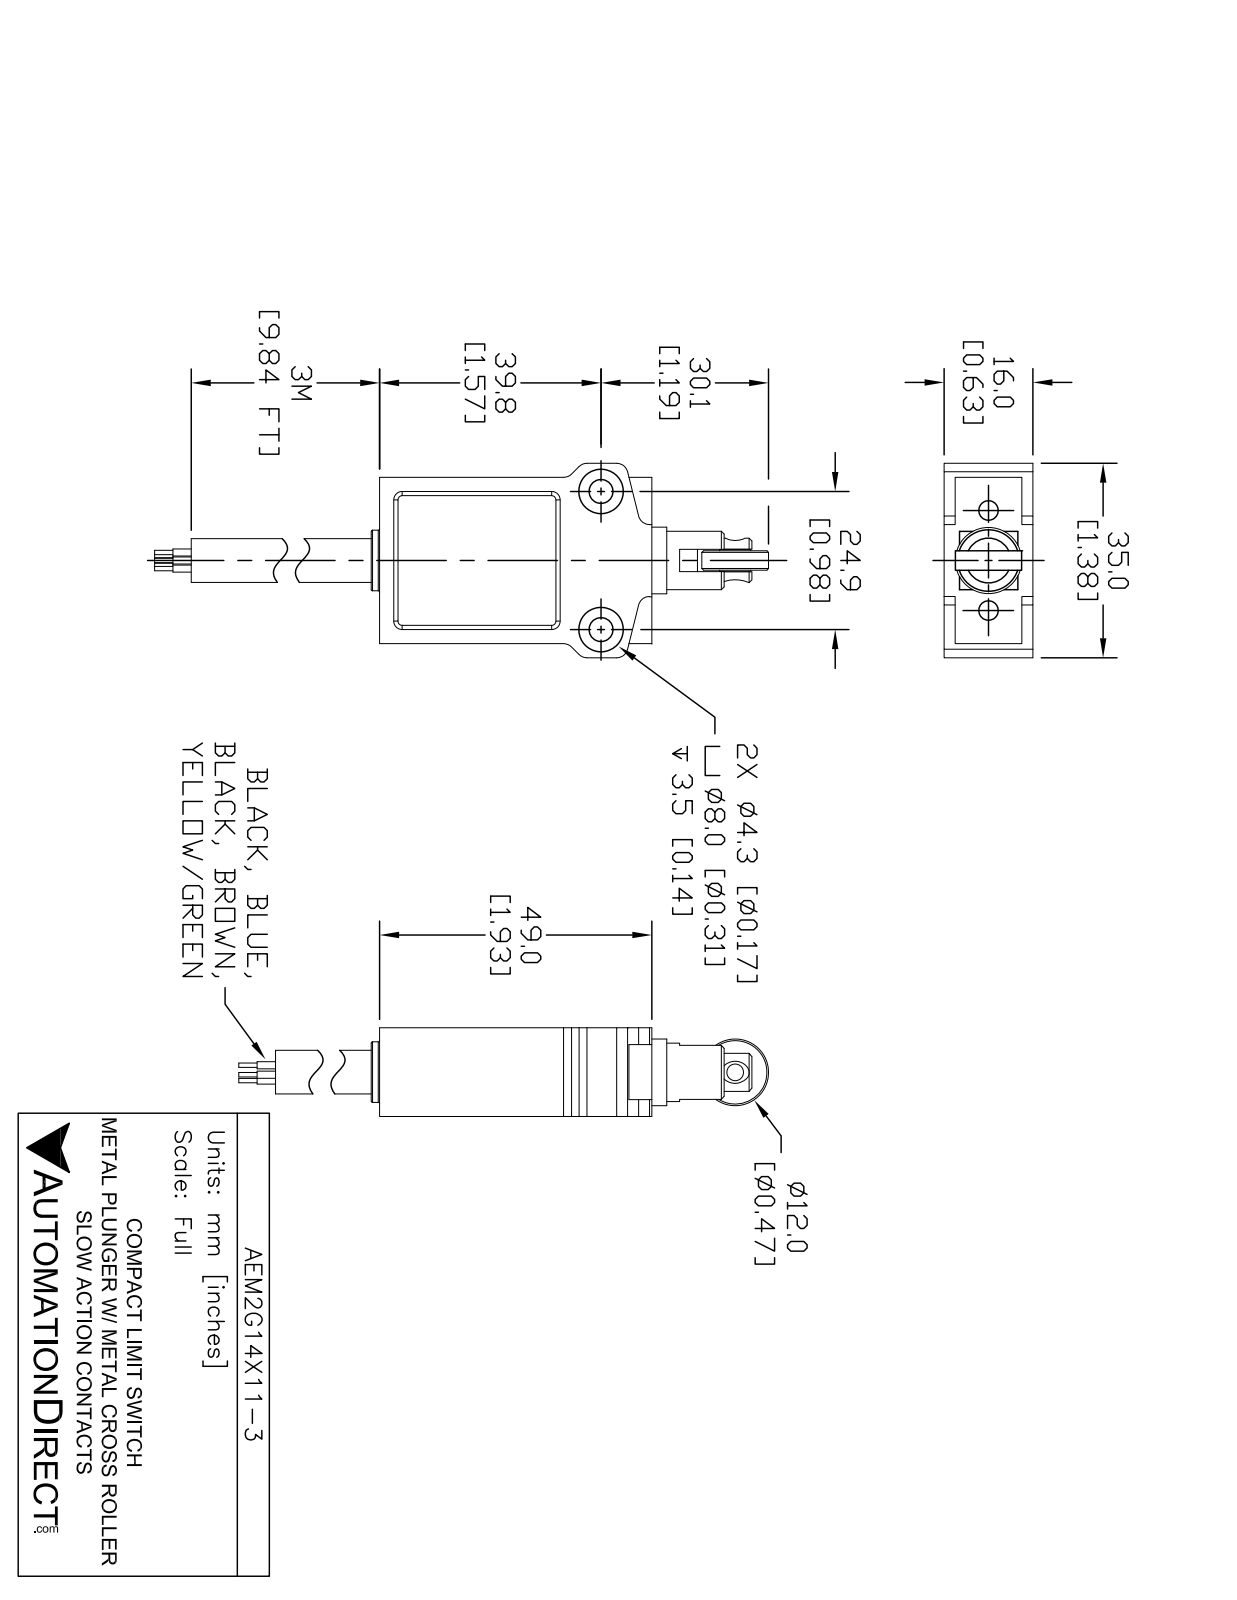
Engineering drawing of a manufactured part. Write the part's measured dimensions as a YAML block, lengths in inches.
part_name: "AEM2G14X11-3_Default"
step_written_by: "SolidWorks 2021 (CONFIG_CONTROL_DESIGN)"
units: inches
bodies: {solids: 2, faces: 119, planar: 56, cylindrical: 43, other: 20}
overall_size: [3.385, 1.38, 0.63]
volume: 1.426
surface_area: 11.99
round_holes:
  - {diameter: 0.138, count: 2}
  - {diameter: 0.177, count: 2}
  - {diameter: 0.344, count: 2}
round_bosses_or_shafts:
  - {diameter: 0.05, count: 5}
  - {diameter: 0.031, count: 5}
  - {diameter: 0.47, count: 2}
  - {diameter: 0.43, count: 1}
  - {diameter: 0.41, count: 1}
  - {diameter: 0.31, count: 1}
partial_cylinders:
  - {radius: 0.03, count: 8}
  - {radius: 0.08, count: 8}
  - {radius: 0.135, count: 1}
face_to_face_distances: [0.03, 0.6, 0.57, 0.63, 1.18, 1.93, 0.51, 0.67, 0.505, 0.675]
hole_center_spacings: [0.7, 0.98]
